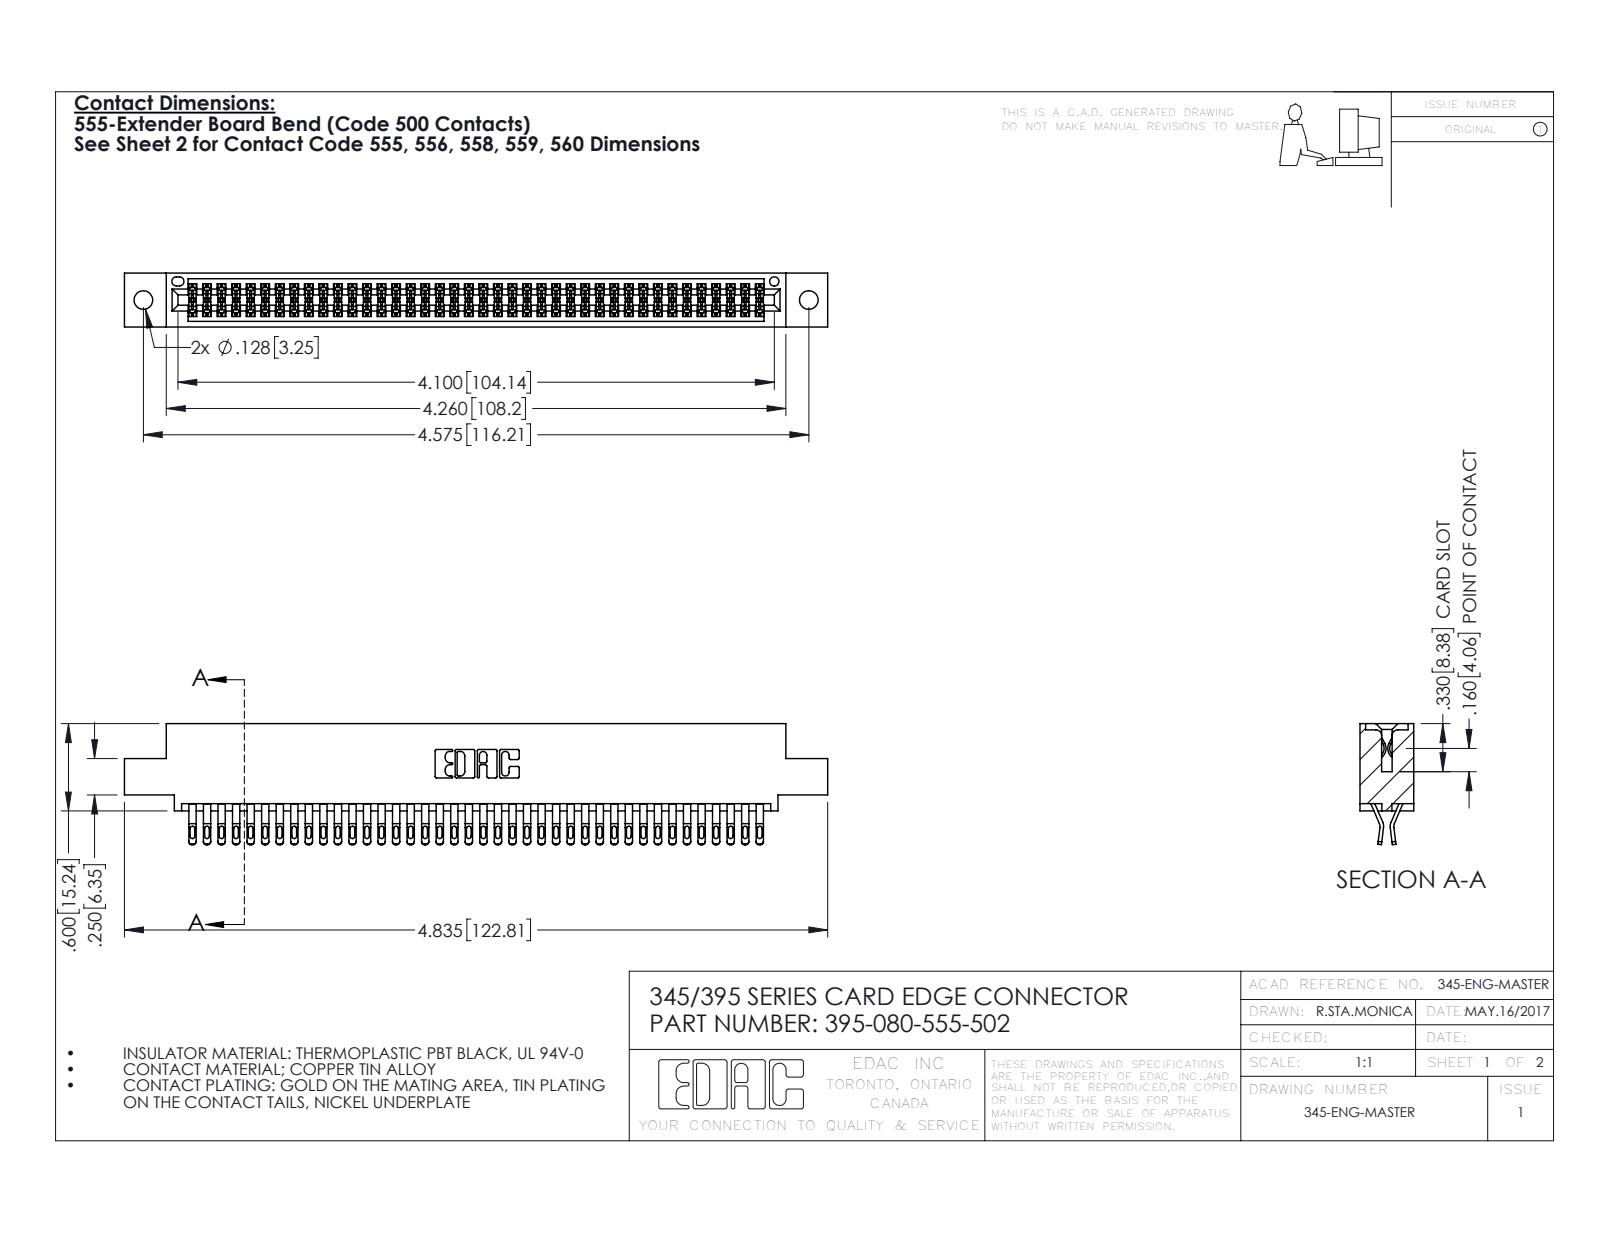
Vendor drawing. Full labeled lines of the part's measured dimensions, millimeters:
Part name (STEP PRODUCT): 395-080-555-502; 345 Part_0.110 Offset - 0.128 Dia; 345-292-001_555 Tail
STEP written by: SolidWorks 2016 (CONFIG_CONTROL_DESIGN)
Units: millimetres
Bodies: 81 solids, 4610 faces (2564 planar, 2046 cylindrical, 0 other)
Overall size (bounding box): 122.8 × 21.1 × 9.4
Volume: 12 000 mm³ · Surface area: 18 370 mm²
Round holes (diameter × count): ⌀3.3 ×2, ⌀1.6 ×1
Partial cylindrical surfaces — rounded edges, fillets, slot ends (radius × count): R0.4 ×200, R0.5 ×160, R0.2 ×120, R0.3 ×22, R0.2 ×6, R0.8 ×6, R0.7 ×3, R0.3 ×2
Main face-to-face distances: 7.6, 1.8, 0.6, 9.4, 5.1, 2.5, 6.9, 5.7, 4.4, 3.8
Hole centre spacings: 6.9, 110.2, 116.2
